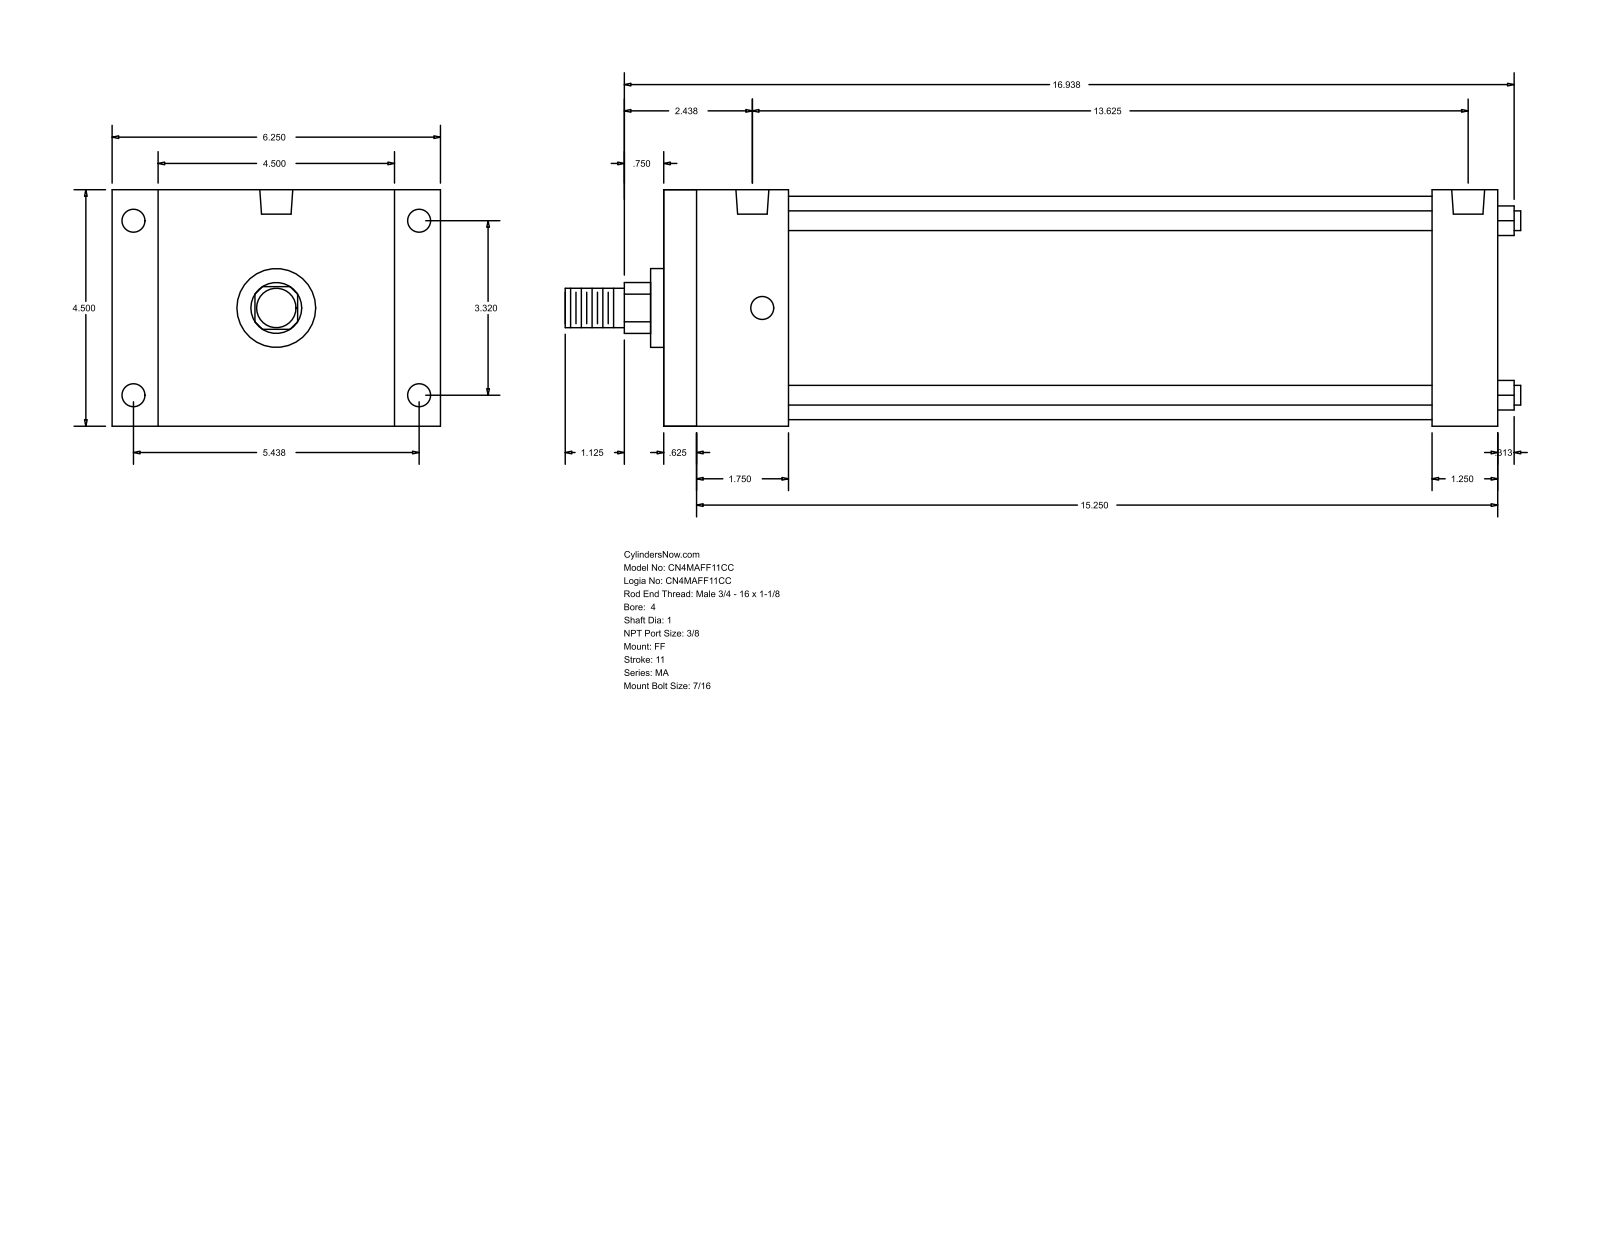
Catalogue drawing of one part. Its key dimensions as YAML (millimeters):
part_name: "MA_FF__0400_1"
step_written_by: "GSSL Pune (CONFIG_CONTROL_DESIGN)"
units: millimeters
bodies: {solids: 0, faces: 92, planar: 64, cylindrical: 28, other: 0}
overall_size: [461.96, 158.75, 114.3]
round_holes:
  - {diameter: 11.11, count: 8}
  - {diameter: 15.93, count: 2}
round_bosses_or_shafts:
  - {diameter: 9.53, count: 4}
  - {diameter: 107.95, count: 1}
  - {diameter: 38.1, count: 1}
  - {diameter: 25.4, count: 1}
  - {diameter: 19.05, count: 1}
partial_cylinders:
  - {radius: 12.29, count: 1}
face_to_face_distances: [114.3, 403.22, 15.87, 387.35, 22.23, 136.53, 371.47, 355.6, 31.75, 60.33]
hole_center_spacings: [4.76, 84.32, 138.12, 161.82, 336.56, 341.32, 346.08]
